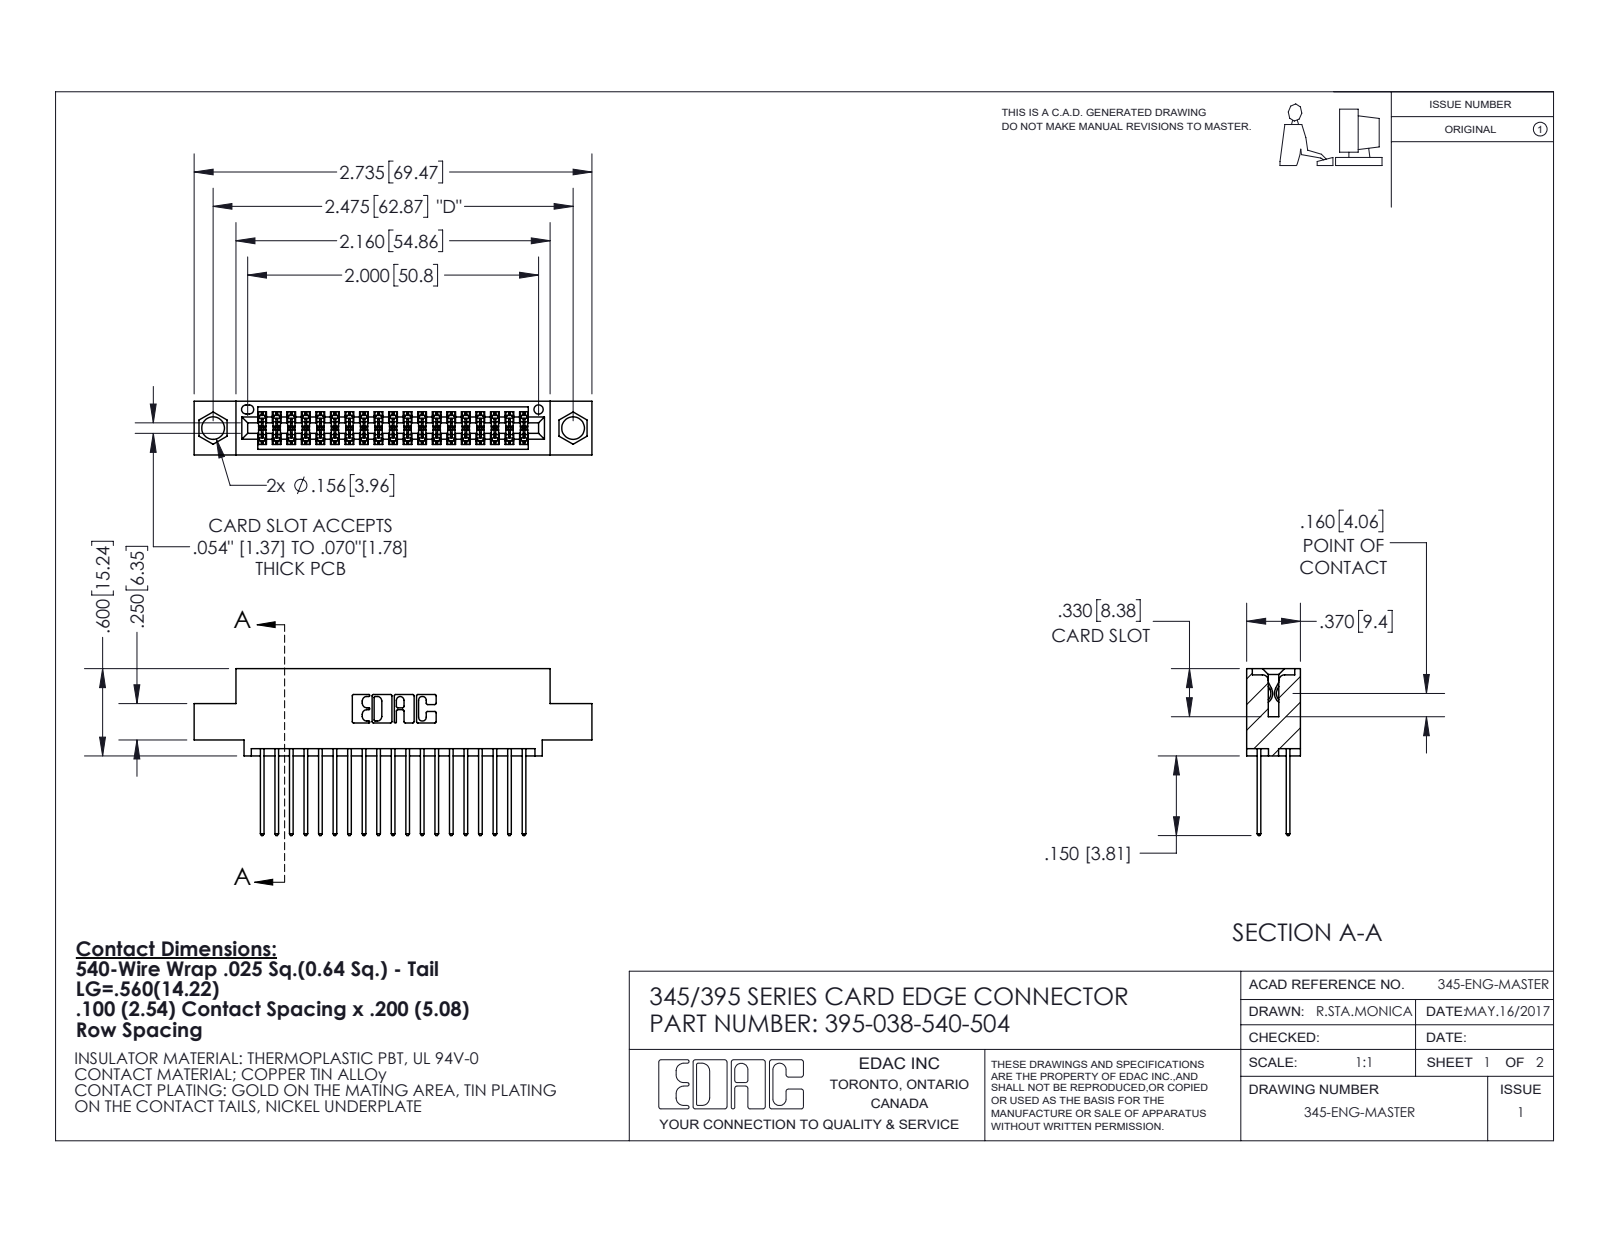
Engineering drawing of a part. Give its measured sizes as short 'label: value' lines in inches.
name: 395-038-540-504; 345-292-001_345-293-140; 345 Part_0.110 Offset - 0.156 Dia-TI
written by: SolidWorks 2020 (CONFIG_CONTROL_DESIGN)
unit: in
bodies: 39 solids, 2044 faces (1352 planar, 692 cylindrical, 0 other)
size: 2.735 × 1.147 × 0.37
volume: 0.397 in³; area: 15.15 in²
holes: 2× ⌀0.156, 1× ⌀0.064
rounds: 57× R0.006, 38× R0.01, 22× R0.01, 6× R0.007, 6× R0.031, 3× R0.026, 2× R0.014, 2× R0.019
face distances: 0.072, 0.298, 0.2, 0.098, 0.272, 0.025, 0.37, 0.225, 0.175, 0.149
hole spacings: 0.27, 2.241, 2.475
